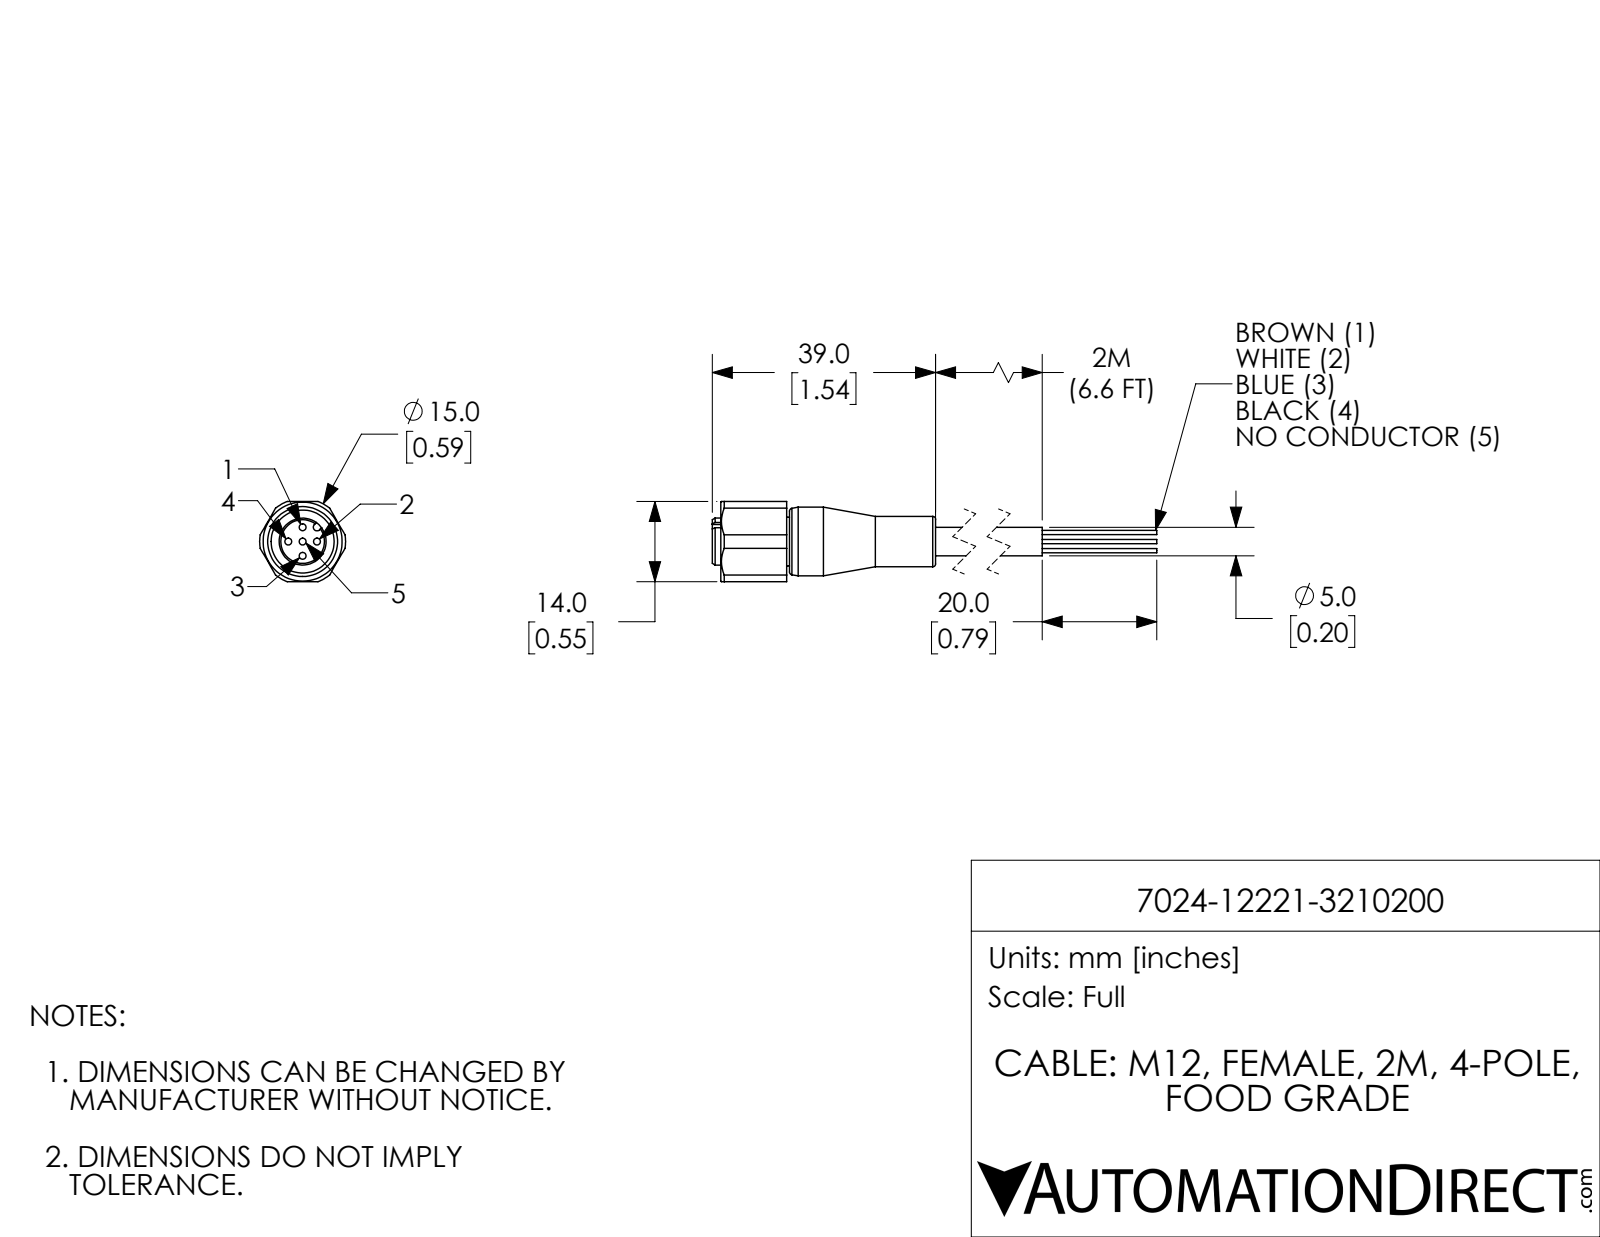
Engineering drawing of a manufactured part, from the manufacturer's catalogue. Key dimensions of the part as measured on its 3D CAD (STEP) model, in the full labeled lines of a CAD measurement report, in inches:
Part name (STEP PRODUCT): 7024-12221-3210200
STEP written by: SolidWorks 2018 (AUTOMOTIVE_DESIGN)
Units: inches
Bodies: 1 solid, 77 faces (25 planar, 37 cylindrical, 15 other)
Overall size (bounding box): 3.063 × 0.591 × 0.551
Volume: 0.251 in³ · Surface area: 4.383 in²
Round holes (diameter × count): ⌀0.047 ×5, ⌀0.433 ×1
Round bosses / shafts (diameter × count): ⌀0.03 ×4, ⌀0.472 ×1, ⌀0.346 ×1, ⌀0.335 ×1, ⌀0.323 ×1, ⌀0.197 ×1
Partial cylindrical surfaces — rounded edges, fillets, slot ends (radius × count): R0.026 ×1, R0.295 ×1
Main face-to-face distances: 0.551, 0.157, 0.354, 0.512, 0.059, 0.295, 0.453, 0.531, 0.472, 0.177
Hole centre spacings: 0.098, 0.139, 0.197
